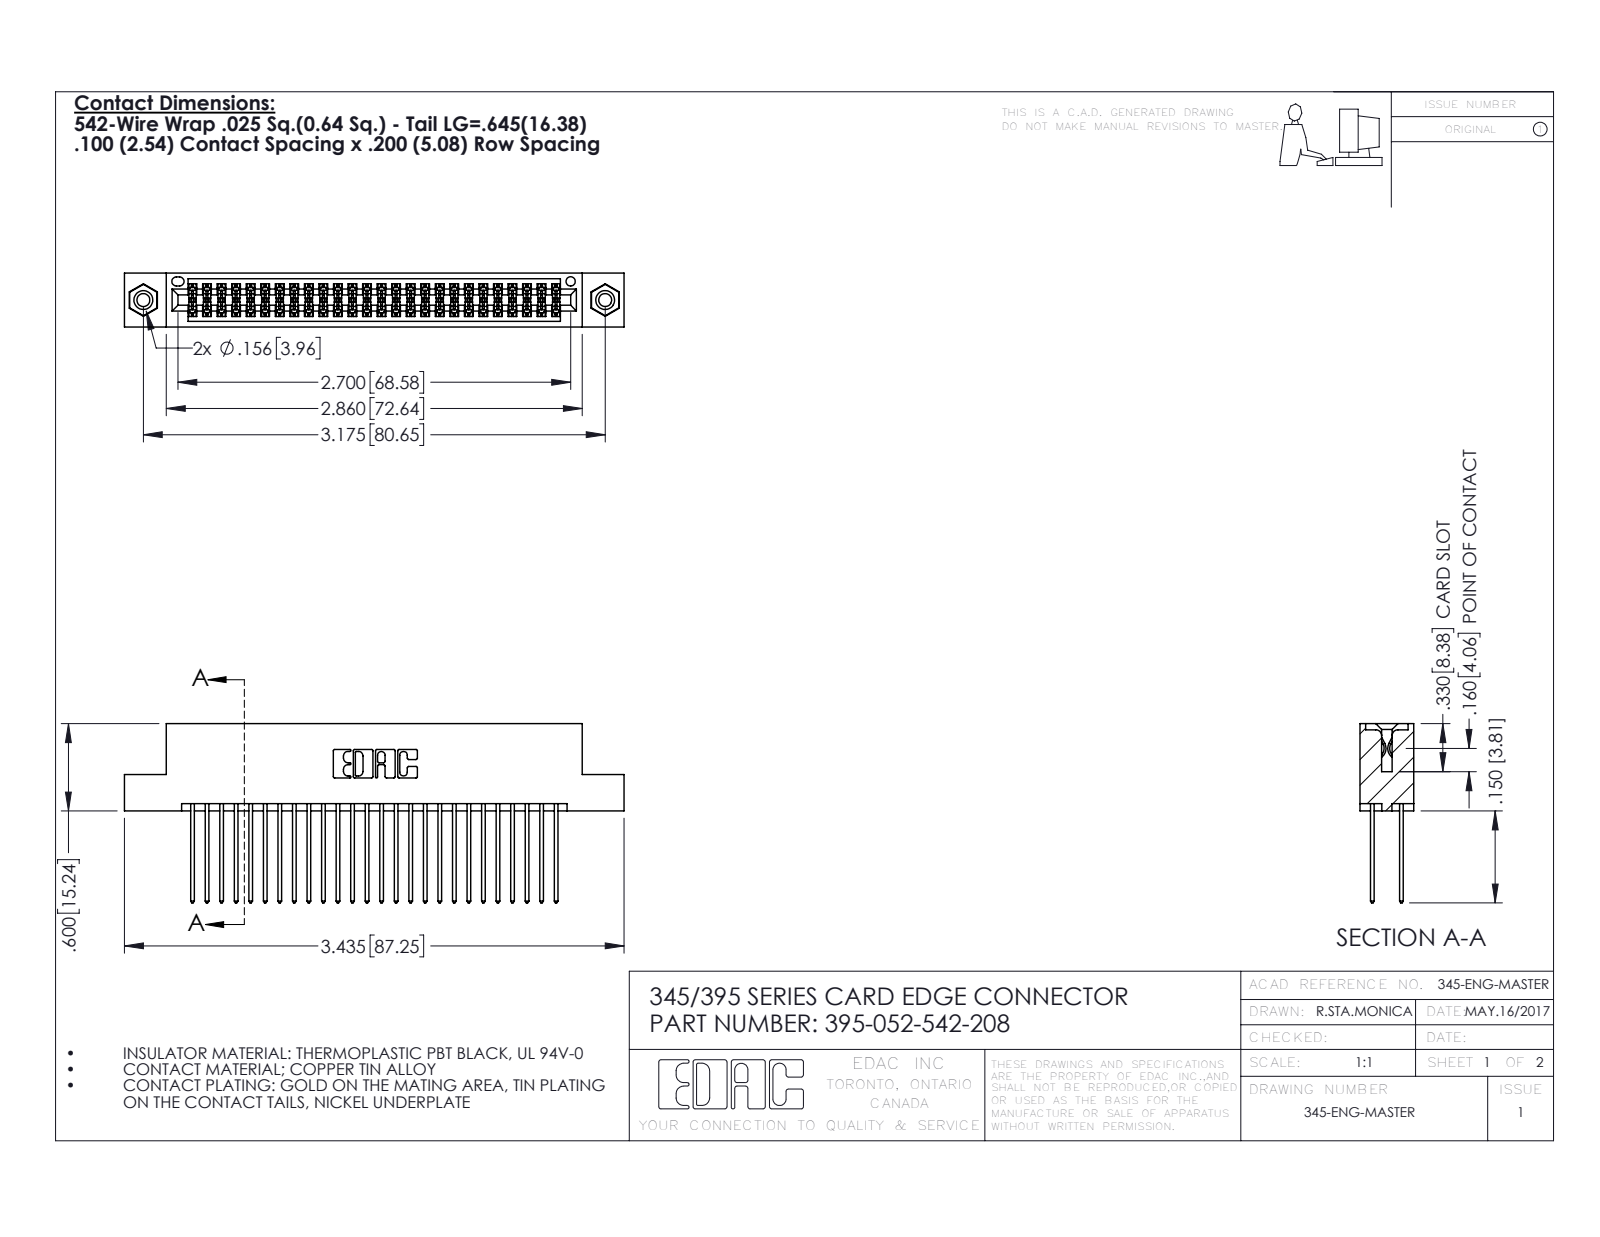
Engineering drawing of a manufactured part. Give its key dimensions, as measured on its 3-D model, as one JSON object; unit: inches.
{"part_name": "345-250-001_345-250-003-102; 395-052-542-208; 345-292-001_345-293-142; 345 Part_Flush Mounting Lugs - 0.156 Dia-TI", "step_written_by": "SolidWorks 2016 (CONFIG_CONTROL_DESIGN)", "units": "inches", "bodies": {"solids": 55, "faces": 2786, "planar": 1828, "cylindrical": 942, "other": 16}, "overall_size": [3.435, 1.232, 0.37], "volume_in3": 0.523, "surface_area_in2": 20.92, "round_holes": [[0.089, 2], [0.125, 2], [0.156, 2], [0.064, 1]], "round_bosses_or_shafts": [[0.155, 2]], "partial_cylinders_radius": [[0.006, 78], [0.01, 52], [0.01, 22], [0.007, 6], [0.031, 6], [0.026, 3], [0.014, 2], [0.019, 2]], "face_to_face_distances": [0.072, 0.298, 0.2, 0.098, 0.272, 0.025, 0.37, 0.225, 0.175, 0.149], "hole_center_spacings": [0.27, 2.94, 3.175]}
